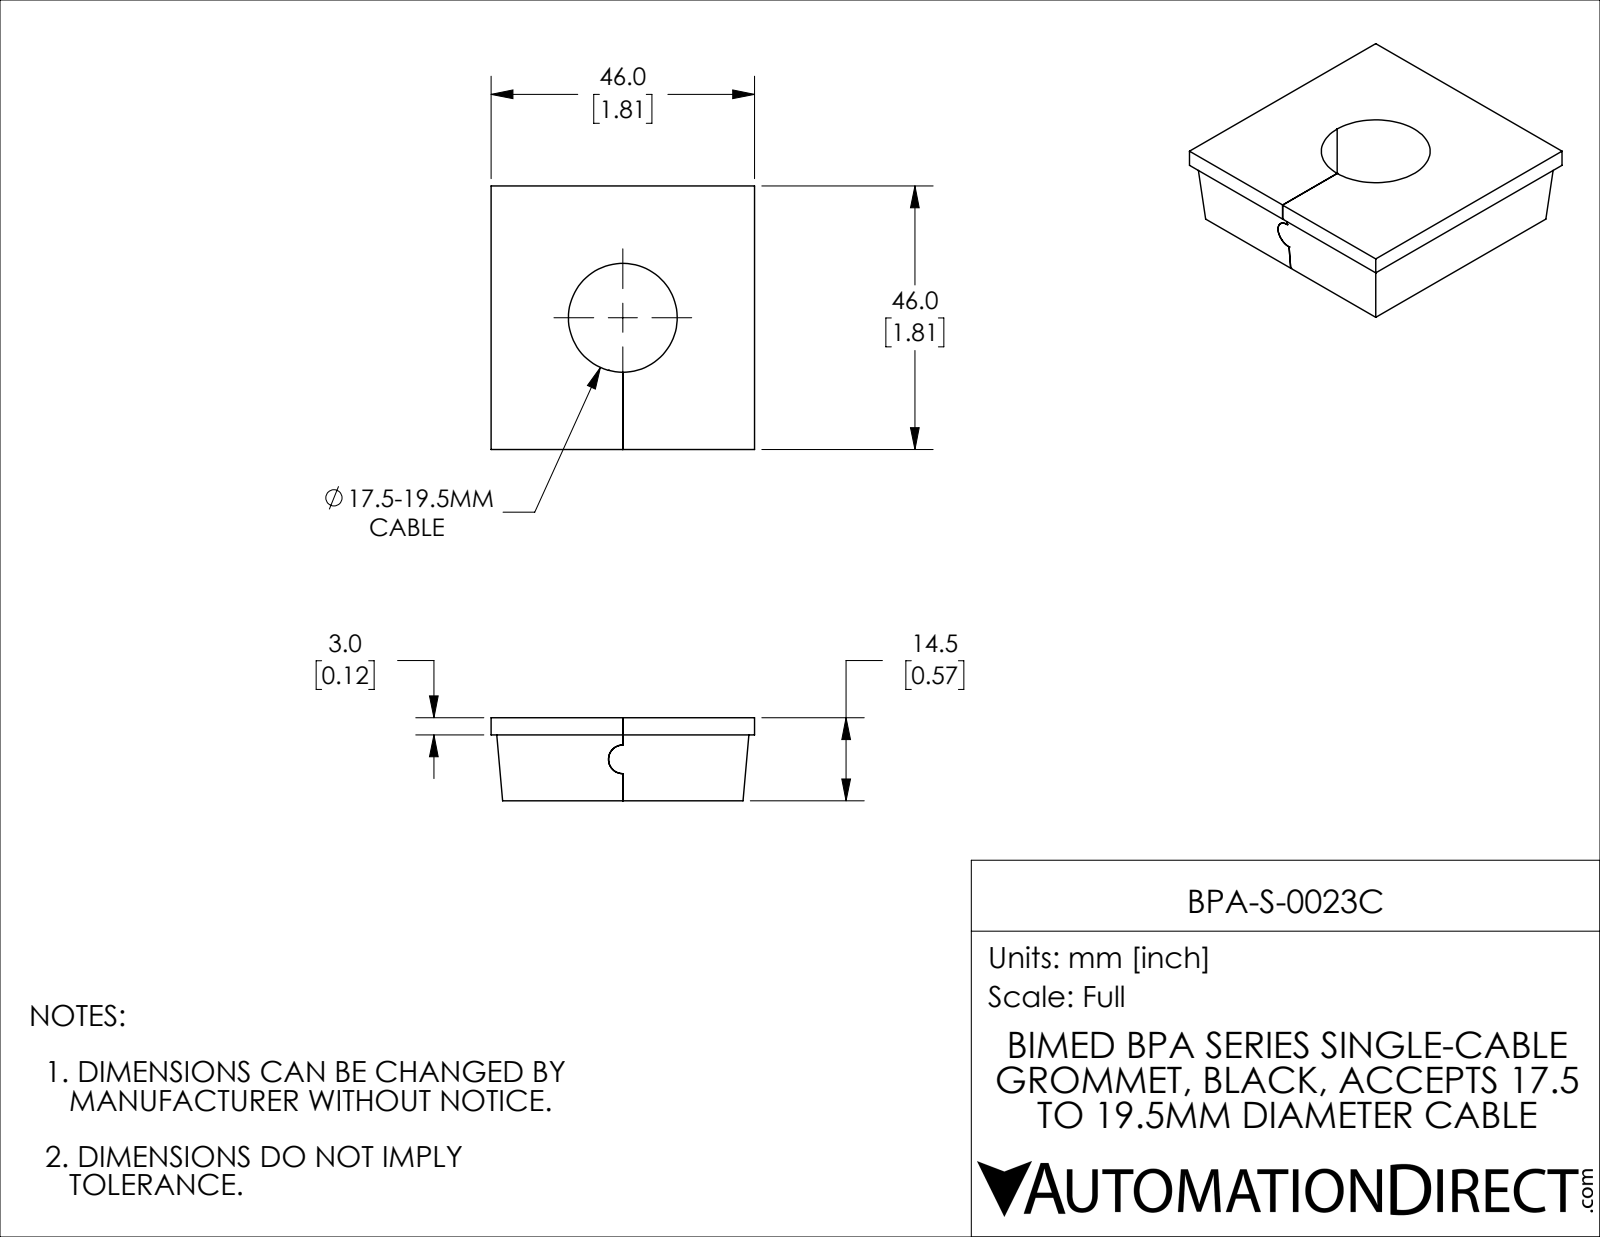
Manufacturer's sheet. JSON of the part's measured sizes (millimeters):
{"part_name": "BPA-S-0023C", "step_written_by": "SolidWorks 2021 (CONFIG_CONTROL_DESIGN)", "units": "millimeters", "bodies": {"solids": 1, "faces": 22, "planar": 17, "cylindrical": 5, "other": 0}, "overall_size": [46, 46, 14.5], "volume_mm3": 23496, "surface_area_mm2": 7323, "round_holes": [[19, 1]], "partial_cylinders_radius": [[2.5, 1], [2.51, 1]], "face_to_face_distances": [14.5, 46, 22.99, 23.01, 11.5, 3]}
